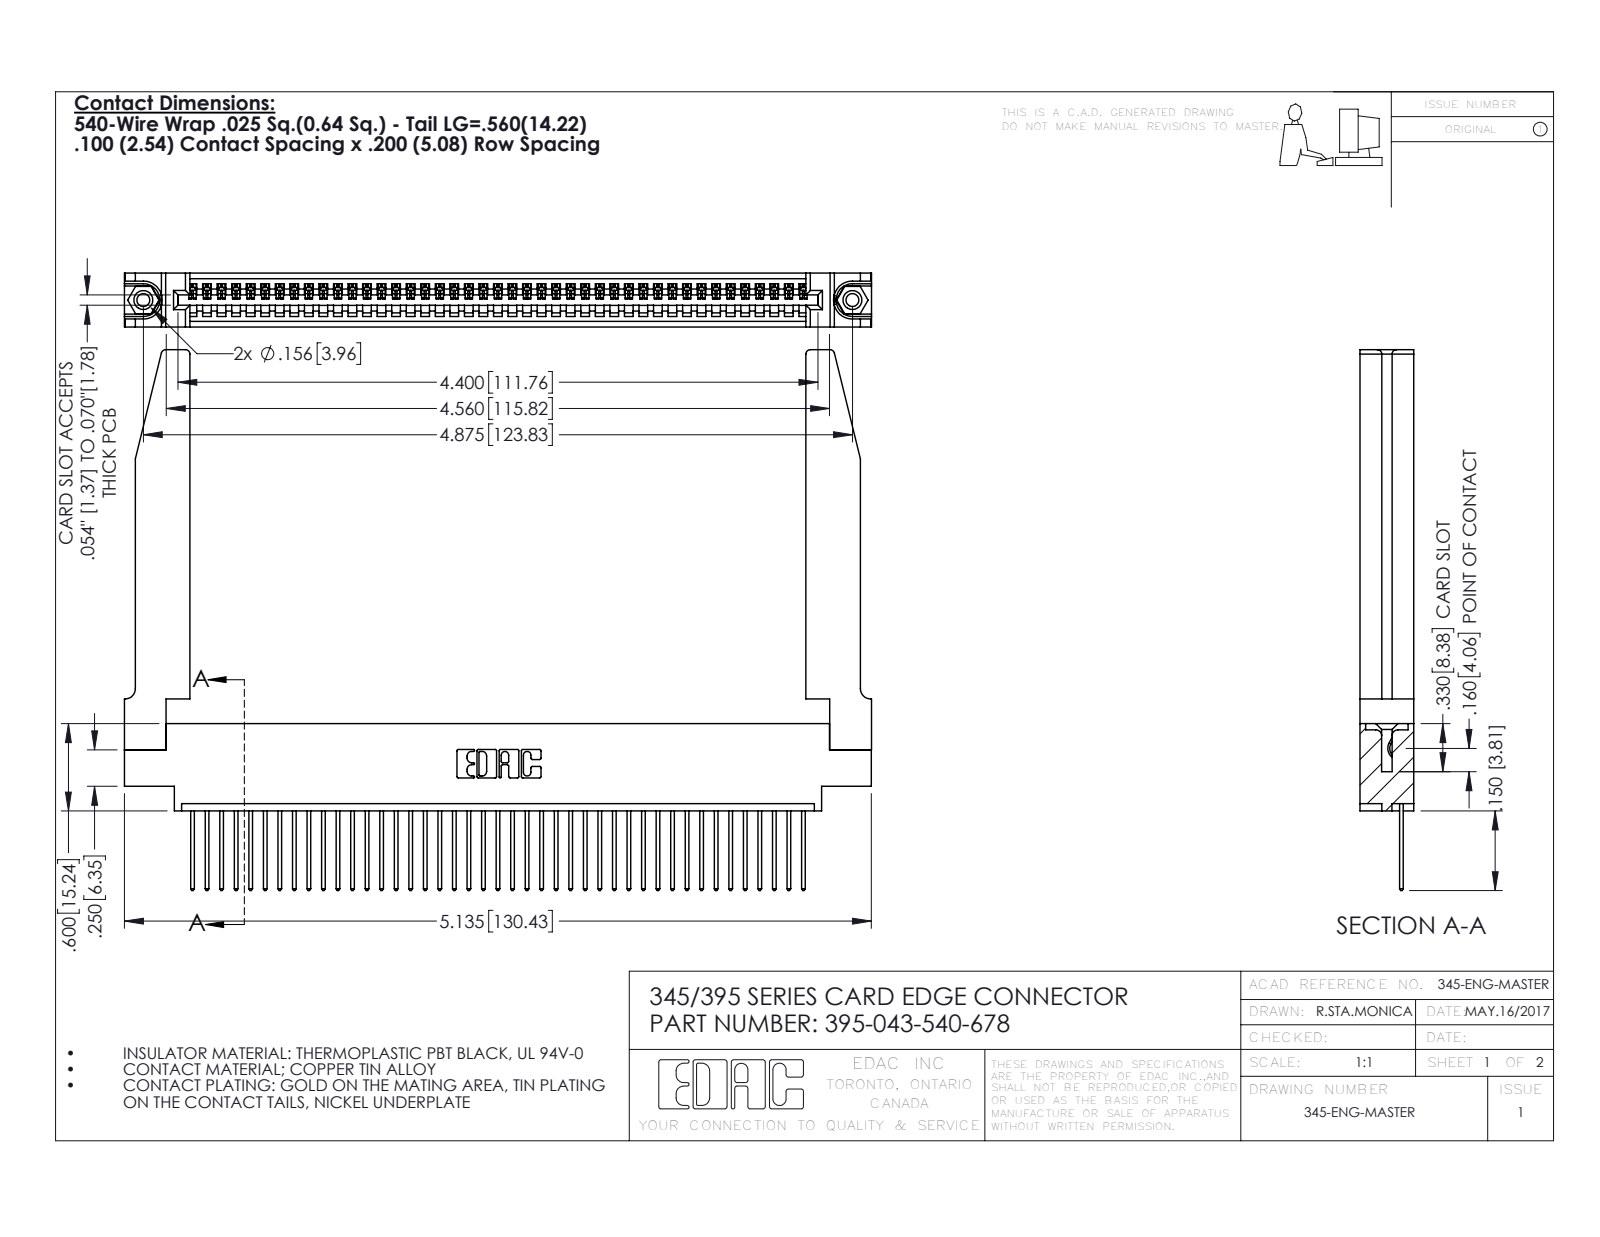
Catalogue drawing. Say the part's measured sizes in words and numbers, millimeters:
The part is named "345-220-078_345-220-078; 345-250-001_345-250-001-102; 345 Part_0.170 Offset - 0.156 Dia-TH; 395-043-540-678 (+1 more)". Its 3-D file was written by "SolidWorks 2016 (CONFIG_CONTROL_DESIGN)". It is 48 solids with 2858 faces: 1946 planar, 860 cylindrical and 52 other. Overall it measures 130.5 by 94.4 by 9.4 millimeters. Its volume is 20 110 cubic millimeters and its surface area 23 810 square millimeters. Round holes: 2 of diameter 2.3, 2 of diameter 3.2, 2 of diameter 4, 1 of diameter 1.6. Round bosses or shafts: 2 of diameter 3.9. Partial cylindrical surfaces (rounded edges, fillets, slot ends): 86 of radius 0.2, 86 of radius 0.3, 22 of radius 0.3, 8 of radius 0.8, 6 of radius 0.2, 6 of radius 0.8, 3 of radius 0.7, 2 of radius 0.8. The main face-to-face distances are 9.4, 1.8, 7.6, 2.5, 6.9, 0.6, 5.1, 5.7, 3.8, 3.8. The hole center spacings are 6.9, 117.8, 123.8.
